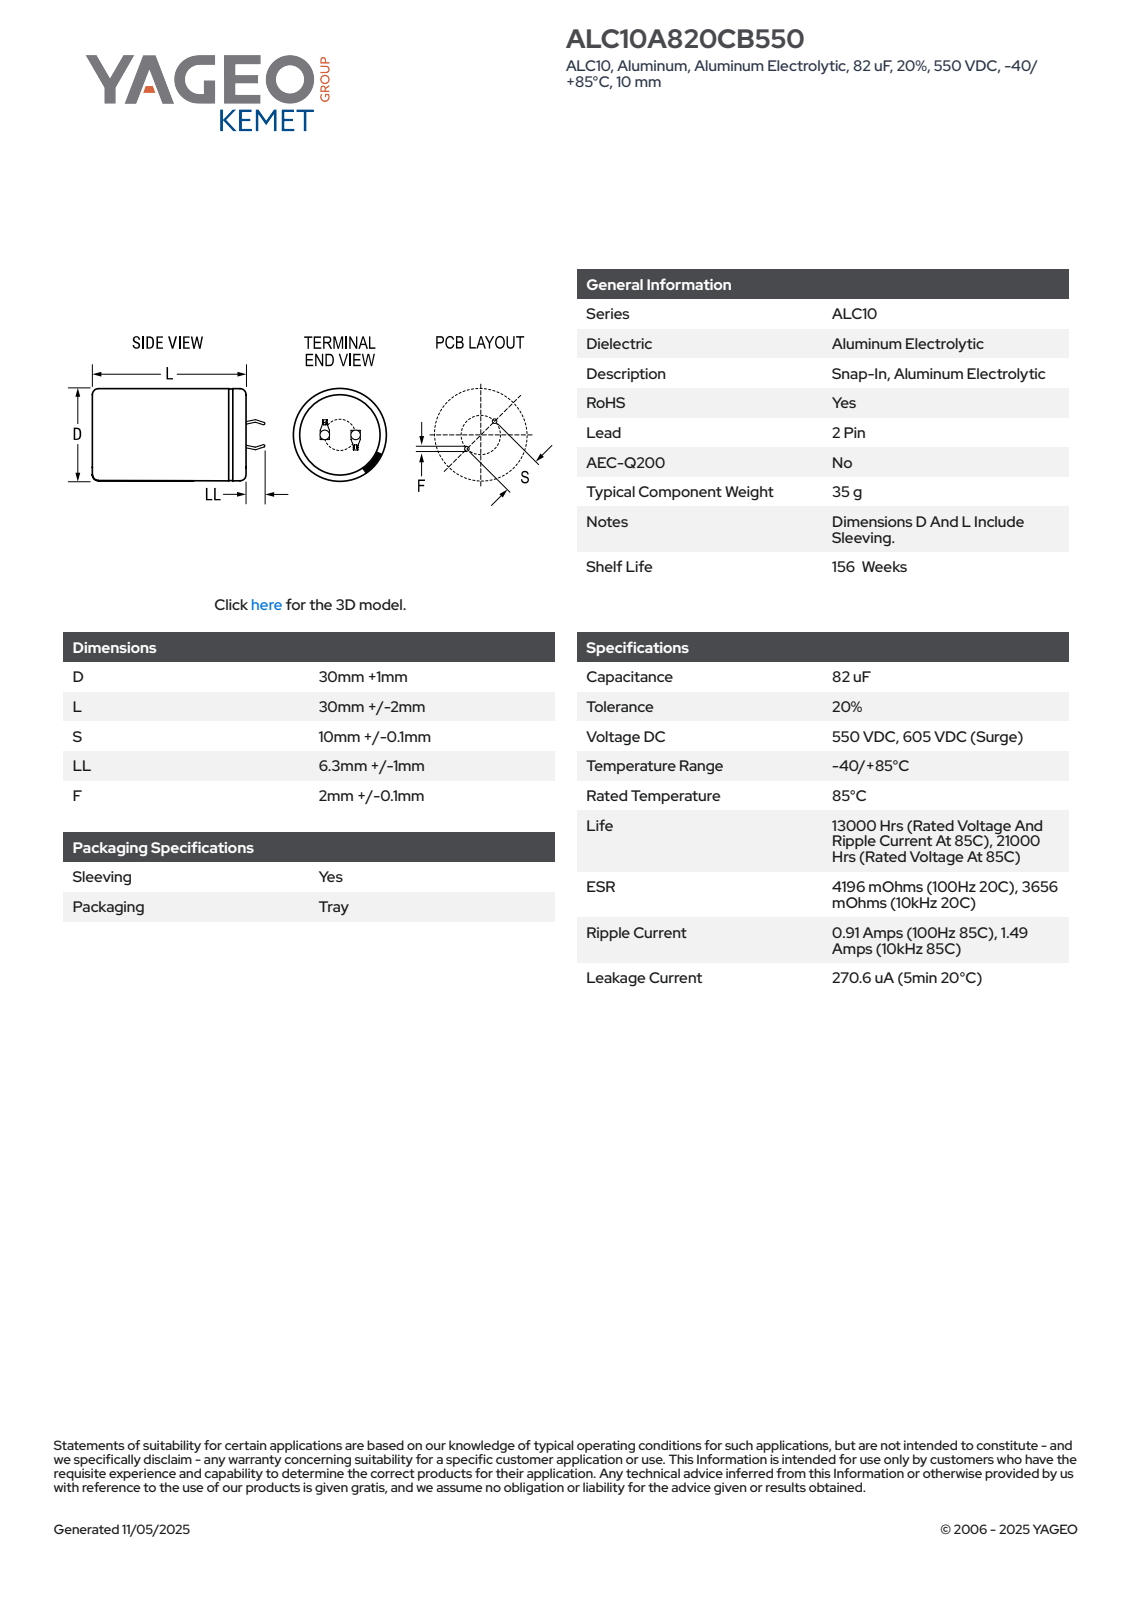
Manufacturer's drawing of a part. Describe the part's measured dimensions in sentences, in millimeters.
The part is named "CARS_K2P_30X30_D31L32S10LL7.3F2.1". Its 3-D file was written by "SolidWorks 2014 (AUTOMOTIVE_DESIGN)". It is 1 solid with 100 faces: 52 planar, 9 cylindrical and 39 other. Overall it measures 39.29 by 31 by 31 millimeters. Its volume is 23 819 cubic millimeters and its surface area 4 636 square millimeters. Round holes: 1 of diameter 27.43. Round bosses or shafts: 1 of diameter 31. Partial cylindrical surfaces (rounded edges, fillets, slot ends): 1 of radius 15.49. The main face-to-face distances are 31.99, 0.6, 32.49, 0.5, 7.08, 7.64, 0.75, 1.35, 7.68, 6.48.
